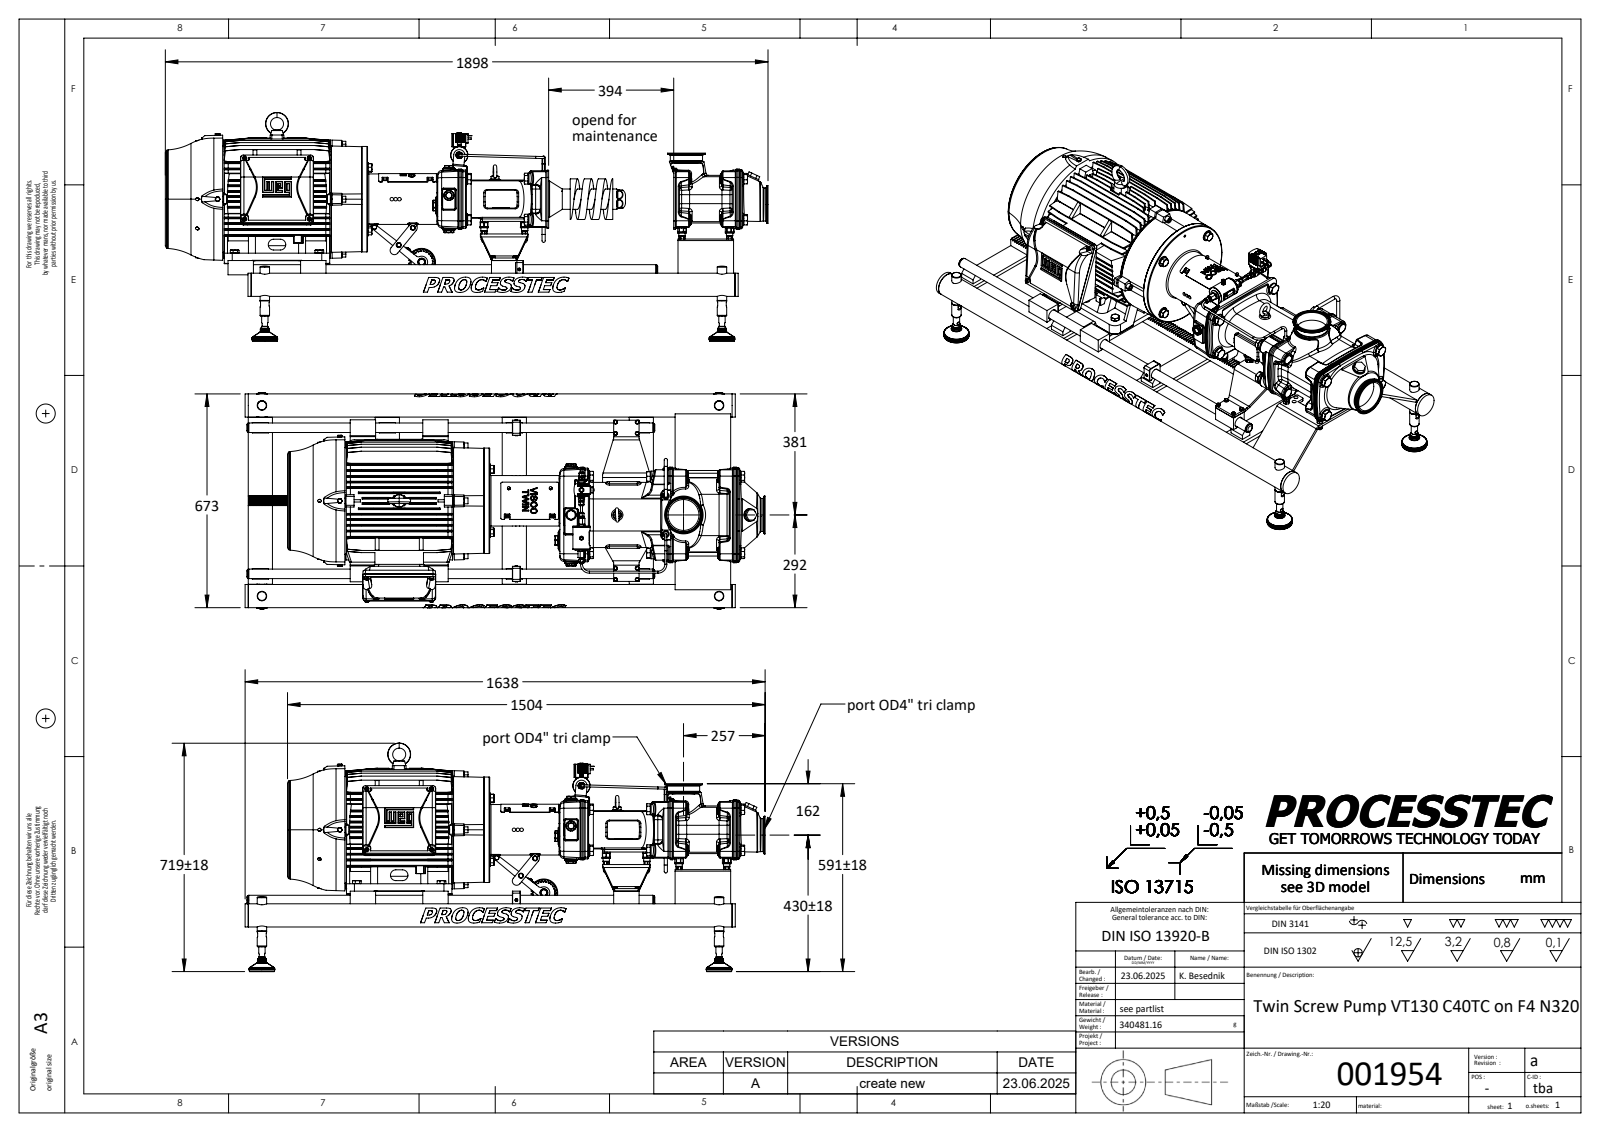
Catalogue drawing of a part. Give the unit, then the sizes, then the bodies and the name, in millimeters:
Units: millimetres
Overall size (bounding box): 1638 × 719.46 × 680.5
Round holes (diameter × count): ⌀8.5 ×21, ⌀5 ×19, ⌀14 ×14, ⌀13 ×13, ⌀17.5 ×13, ⌀6.8 ×12, ⌀4.1 ×11, ⌀11 ×11, ⌀8 ×9, ⌀10.5 ×9, ⌀6.4 ×8, ⌀10.1 ×8
Round bosses / shafts (diameter × count): ⌀10 ×33, ⌀6 ×19, ⌀24 ×17, ⌀20 ×16, ⌀8 ×13, ⌀18.5 ×12, ⌀17 ×11, ⌀16 ×11
Partial cylindrical surfaces — rounded edges, fillets, slot ends (radius × count): R2.98 ×188, R3 ×81, R1.5 ×54, R0.48 ×50, R6 ×48, R2 ×39, R8 ×27, R4 ×19
Main face-to-face distances: 342.3, 12.7, 8, 747.8, 405.5, 784.5, 444.3, 102, 303.5, 1228.8
Hole centre spacings: 461.41, 400, 129.3, 230, 832.41, 55, 609.59, 800
Volume: 100 300 000 mm³ · Surface area: 8 307 000 mm²
Bodies: 210 solids, 14196 faces (4710 planar, 3777 cylindrical, 5709 other)
Part name (STEP PRODUCT): 001014; 001593; Teil4^001381; 001017 (+8 more)
STEP written by: SolidWorks 2023 (AUTOMOTIVE_DESIGN)
